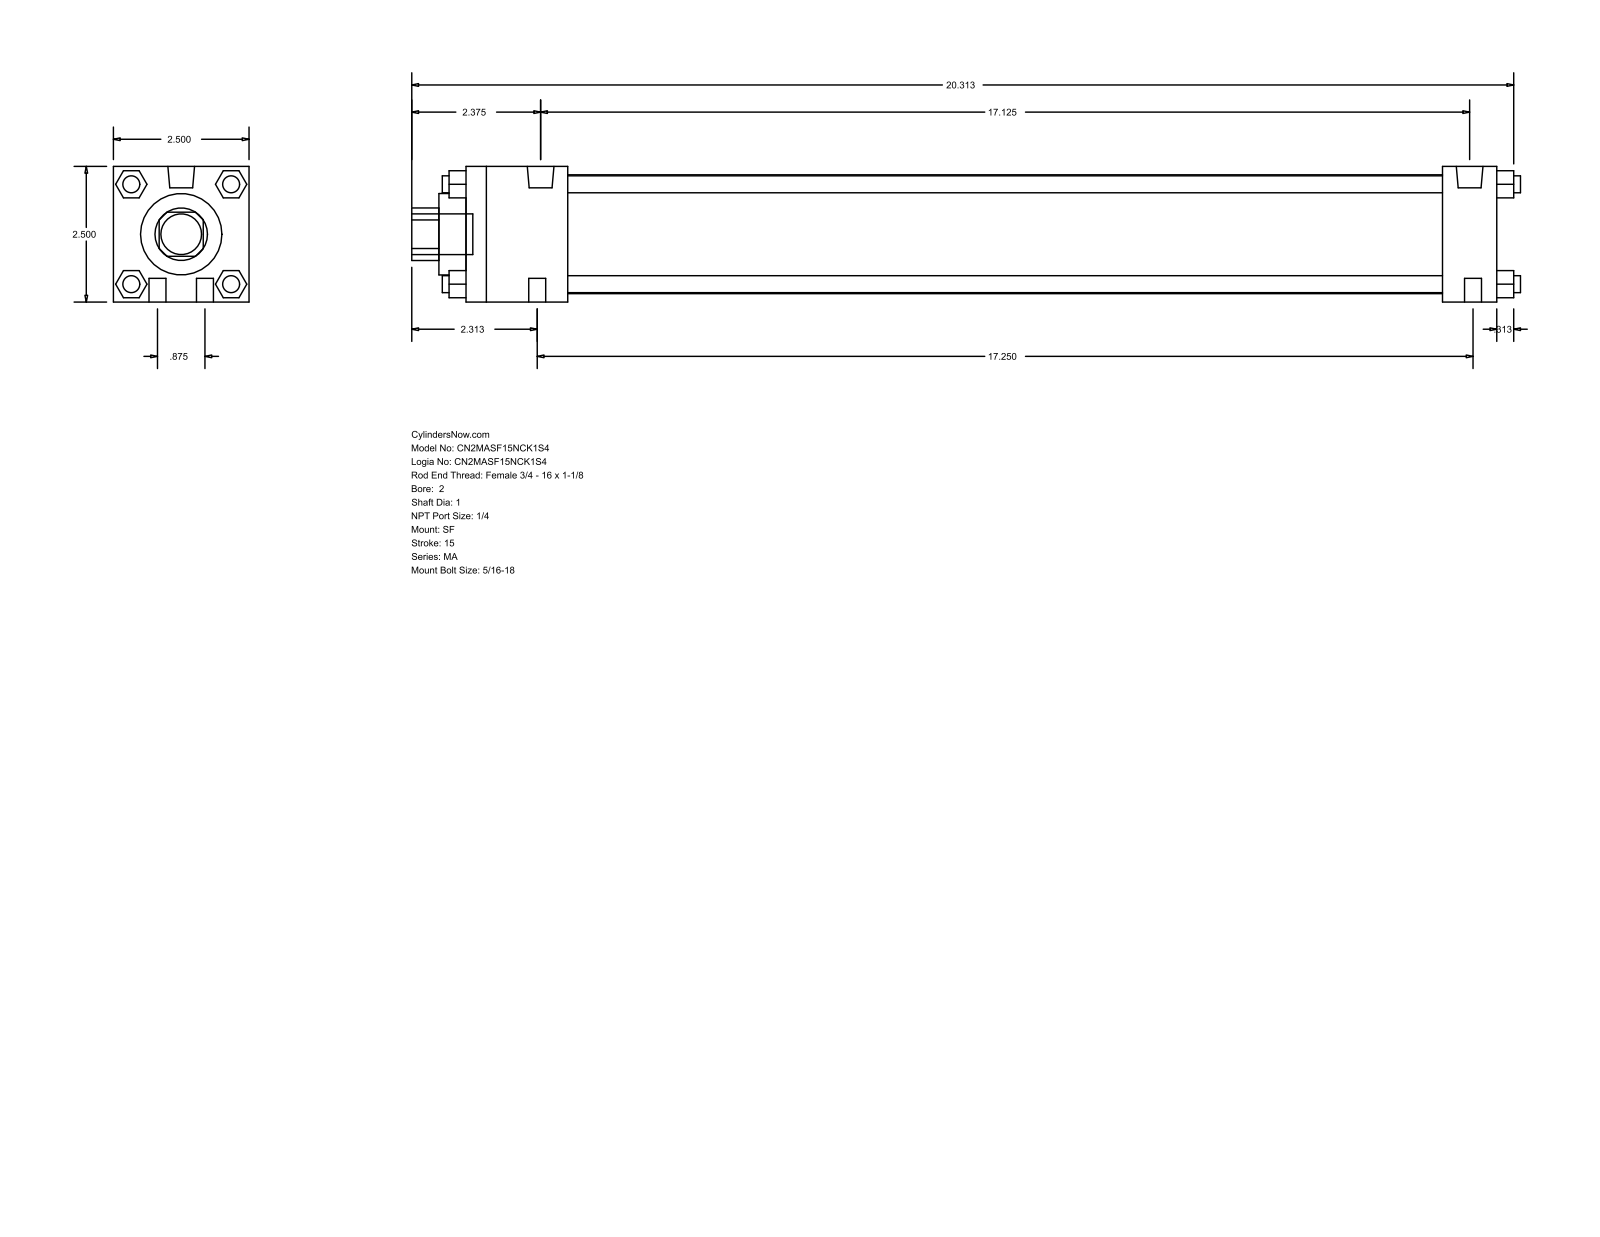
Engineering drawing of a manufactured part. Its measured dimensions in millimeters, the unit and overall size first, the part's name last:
Units: millimetres
Overall size (bounding box): 519.11 × 63.5 × 63.5
Round holes (diameter × count): ⌀25.4 ×1, ⌀38.1 ×1, ⌀55.63 ×1
Round bosses / shafts (diameter × count): ⌀7.94 ×10, ⌀12.49 ×2, ⌀19.05 ×1
Partial cylindrical surfaces — rounded edges, fillets, slot ends (radius × count): R12.29 ×1
Main face-to-face distances: 63.5, 482.6, 12.7, 25.4, 457.2, 47.63, 409.57, 434.97, 23.37, 40.47
Bodies: 0 solids, 124 faces (94 planar, 30 cylindrical, 0 other)
Part name (STEP PRODUCT): MA_SF__0200_1
STEP written by: GSSL Pune (CONFIG_CONTROL_DESIGN)
